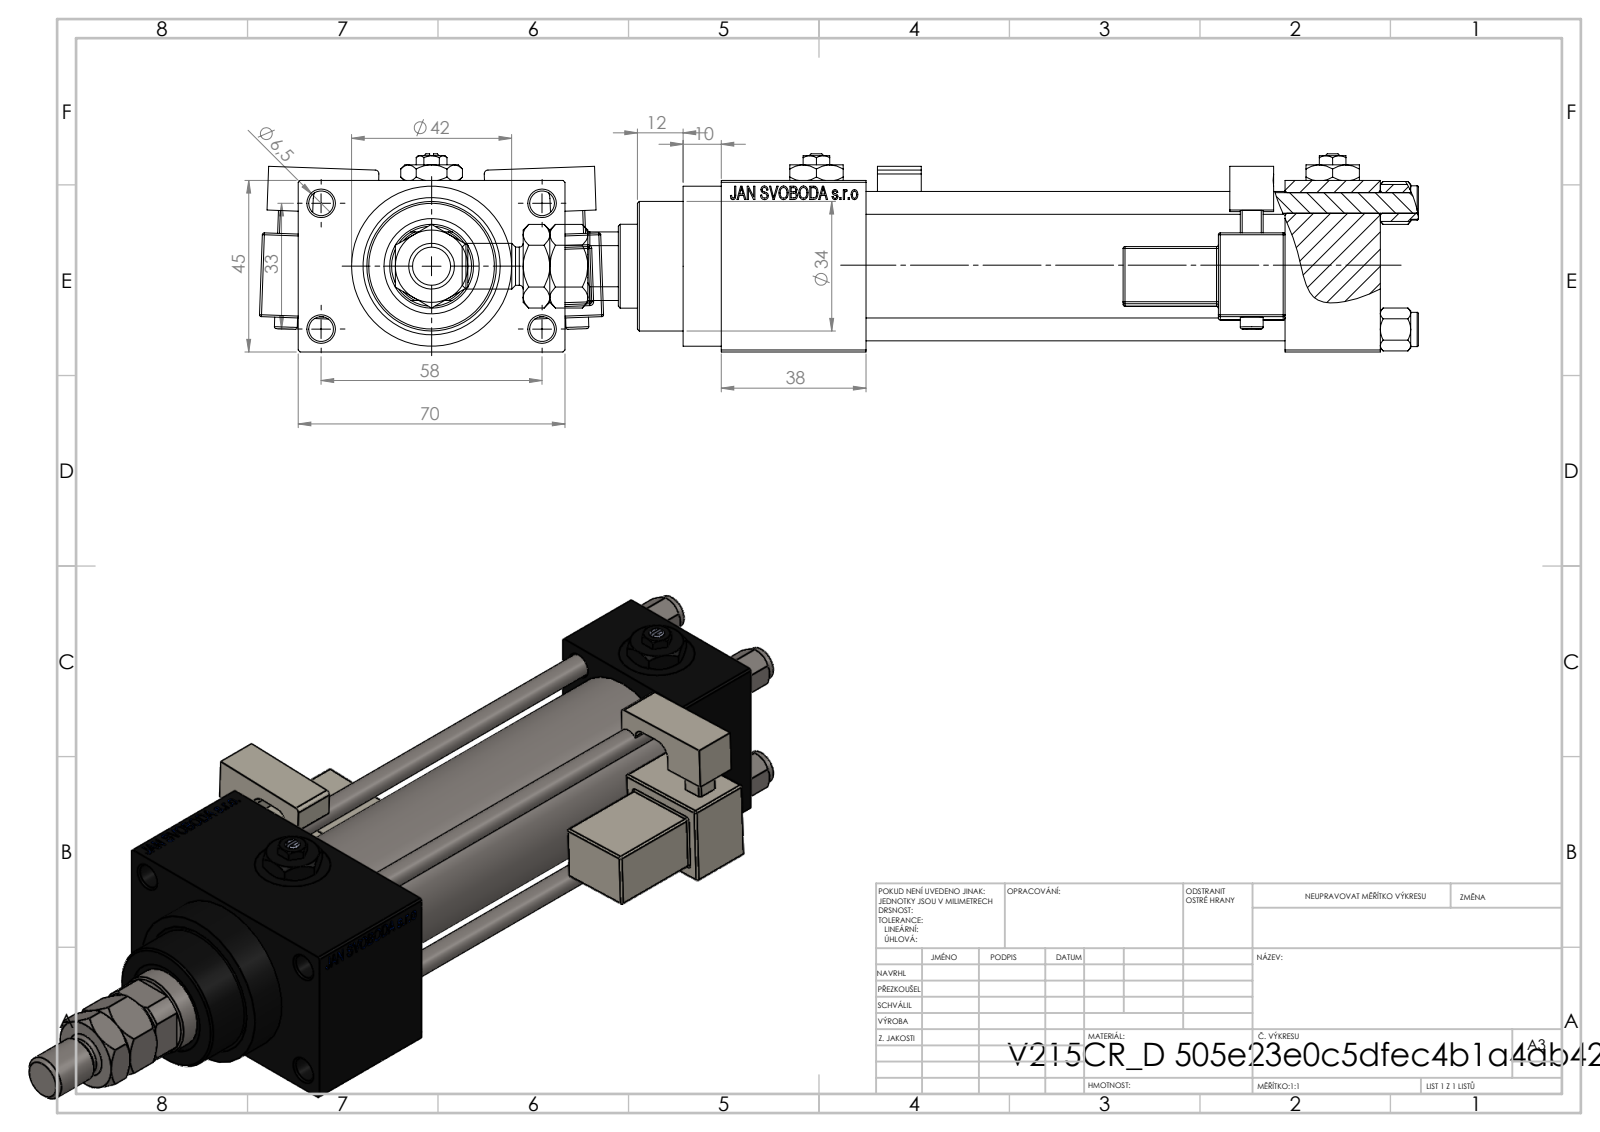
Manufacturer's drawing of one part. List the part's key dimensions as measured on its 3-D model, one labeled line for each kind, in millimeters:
Part name (STEP PRODUCT): V215_VC_A; V215CR_VCP_D; Zatka_pro_OIL_PORT; MTA (+4 more)
STEP written by: SolidWorks 2019 (CONFIG_CONTROL_DESIGN)
Units: millimetres
Bodies: 16 solids, 1411 faces (619 planar, 164 cylindrical, 628 other)
Overall size (bounding box): 251 × 90.31 × 52
Volume: 340 266 mm³ · Surface area: 117 295 mm²
Round holes (diameter × count): ⌀6 ×4, ⌀6.5 ×4, ⌀7 ×2, ⌀13.16 ×2, ⌀20 ×2, ⌀10.5 ×1, ⌀22 ×1, ⌀24 ×1, ⌀25 ×1, ⌀32 ×1, ⌀33 ×1
Round bosses / shafts (diameter × count): ⌀9 ×4, ⌀6 ×2, ⌀42 ×1, ⌀38 ×1, ⌀34 ×1, ⌀12 ×1, ⌀10 ×1
Partial cylindrical surfaces — rounded edges, fillets, slot ends (radius × count): R0.5 ×48, R1 ×2, R2.5 ×2, R4 ×2, R10.5 ×1
Main face-to-face distances: 45, 25, 12.5, 110, 3, 57.5, 135, 38, 148, 70
Hole centre spacings: 12.4, 23.48, 33.2, 33.37, 35.35, 45.6, 56.35, 33
